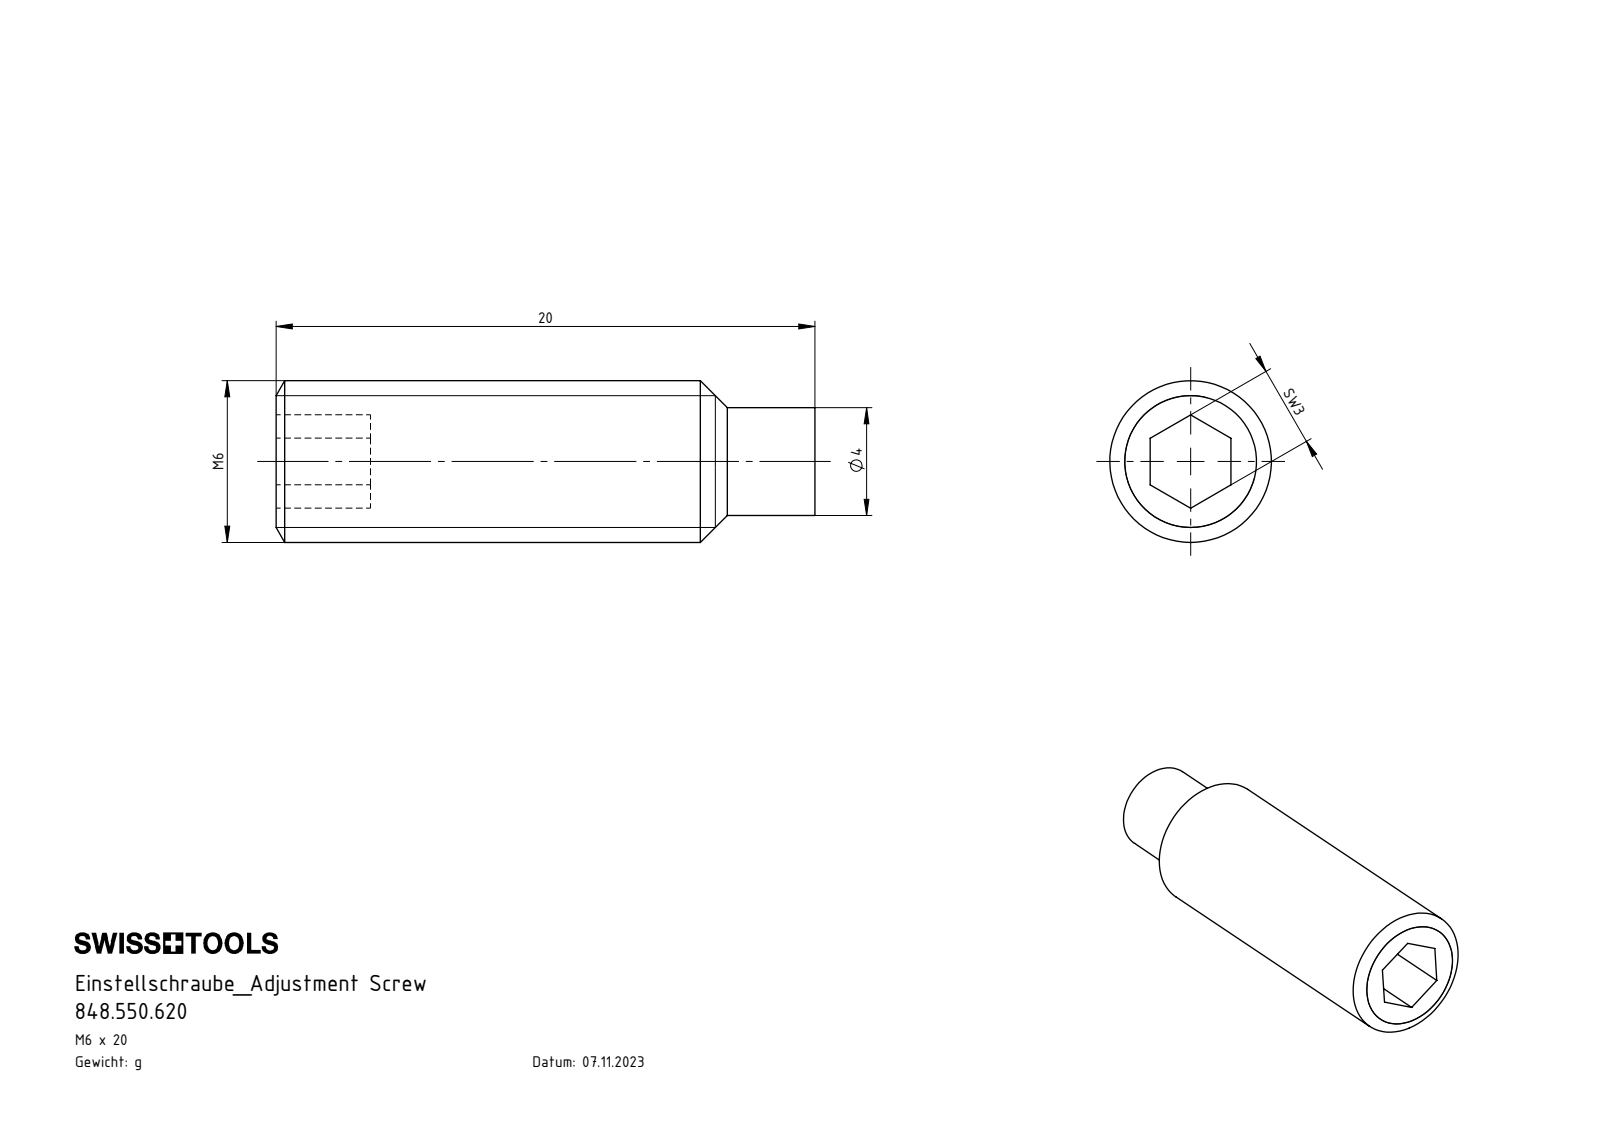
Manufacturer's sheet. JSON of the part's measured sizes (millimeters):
{"part_name": "848.550.620", "step_written_by": "SolidWorks 2022 (AUTOMOTIVE_DESIGN)", "units": "millimeters", "bodies": {"solids": 1, "faces": 17, "planar": 9, "cylindrical": 4, "other": 4}, "overall_size": [20, 6, 6], "volume_mm3": 477, "surface_area_mm2": 433, "round_bosses_or_shafts": [[6, 1], [4, 1]], "face_to_face_distances": [3, 20, 3.5, 16.5]}
